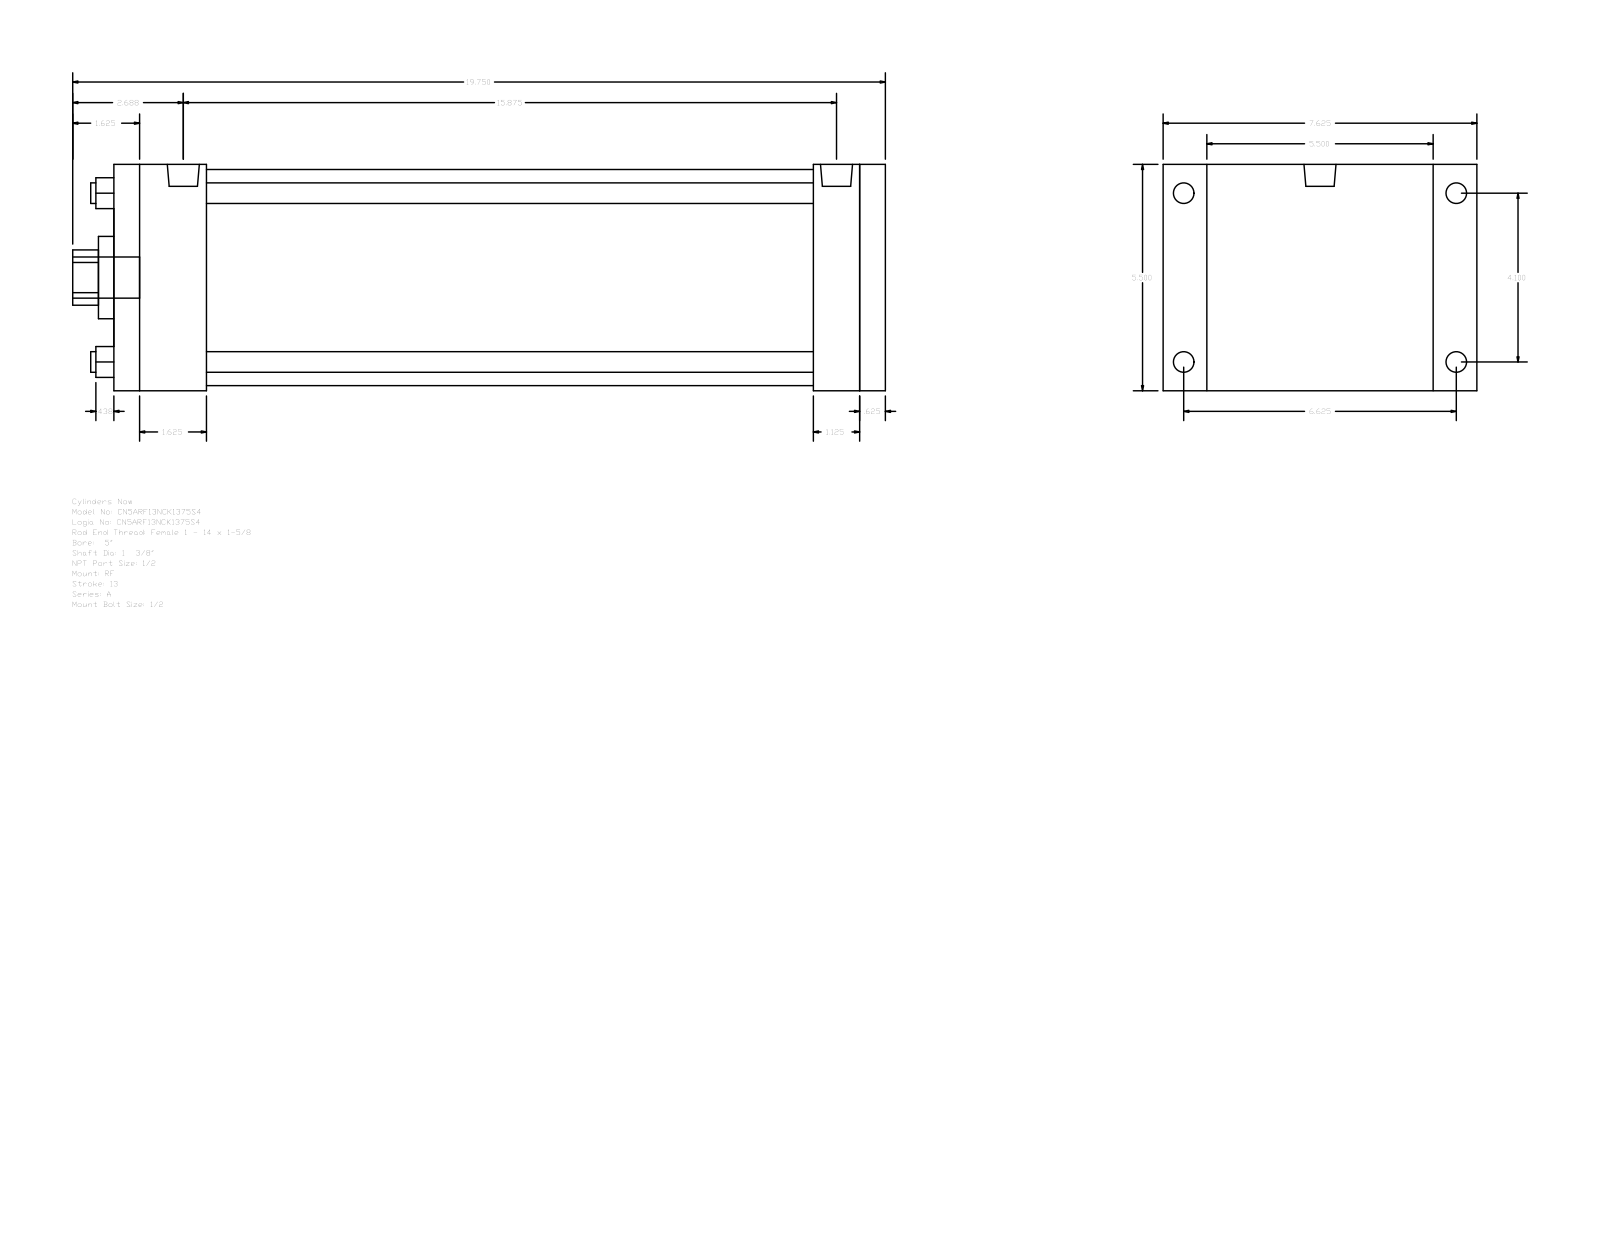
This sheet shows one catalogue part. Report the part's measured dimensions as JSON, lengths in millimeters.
{"part_name": "A_RF__0500_1.375", "step_written_by": "GSSL Pune (CONFIG_CONTROL_DESIGN)", "units": "millimeters", "bodies": {"solids": 0, "faces": 92, "planar": 64, "cylindrical": 28, "other": 0}, "overall_size": [501.65, 193.68, 139.7], "round_holes": [[12.7, 4], [34.92, 1], [50.8, 1], [133.35, 1]], "round_bosses_or_shafts": [[12.7, 4], [8.73, 4], [19.77, 2], [25.4, 1]], "partial_cylinders_radius": [[17.06, 1]], "face_to_face_distances": [139.7, 476.25, 15.88, 460.37, 28.57, 57.15, 403.22, 419.1, 431.8, 374.65], "hole_center_spacings": [73.64, 104.14, 147.28]}
